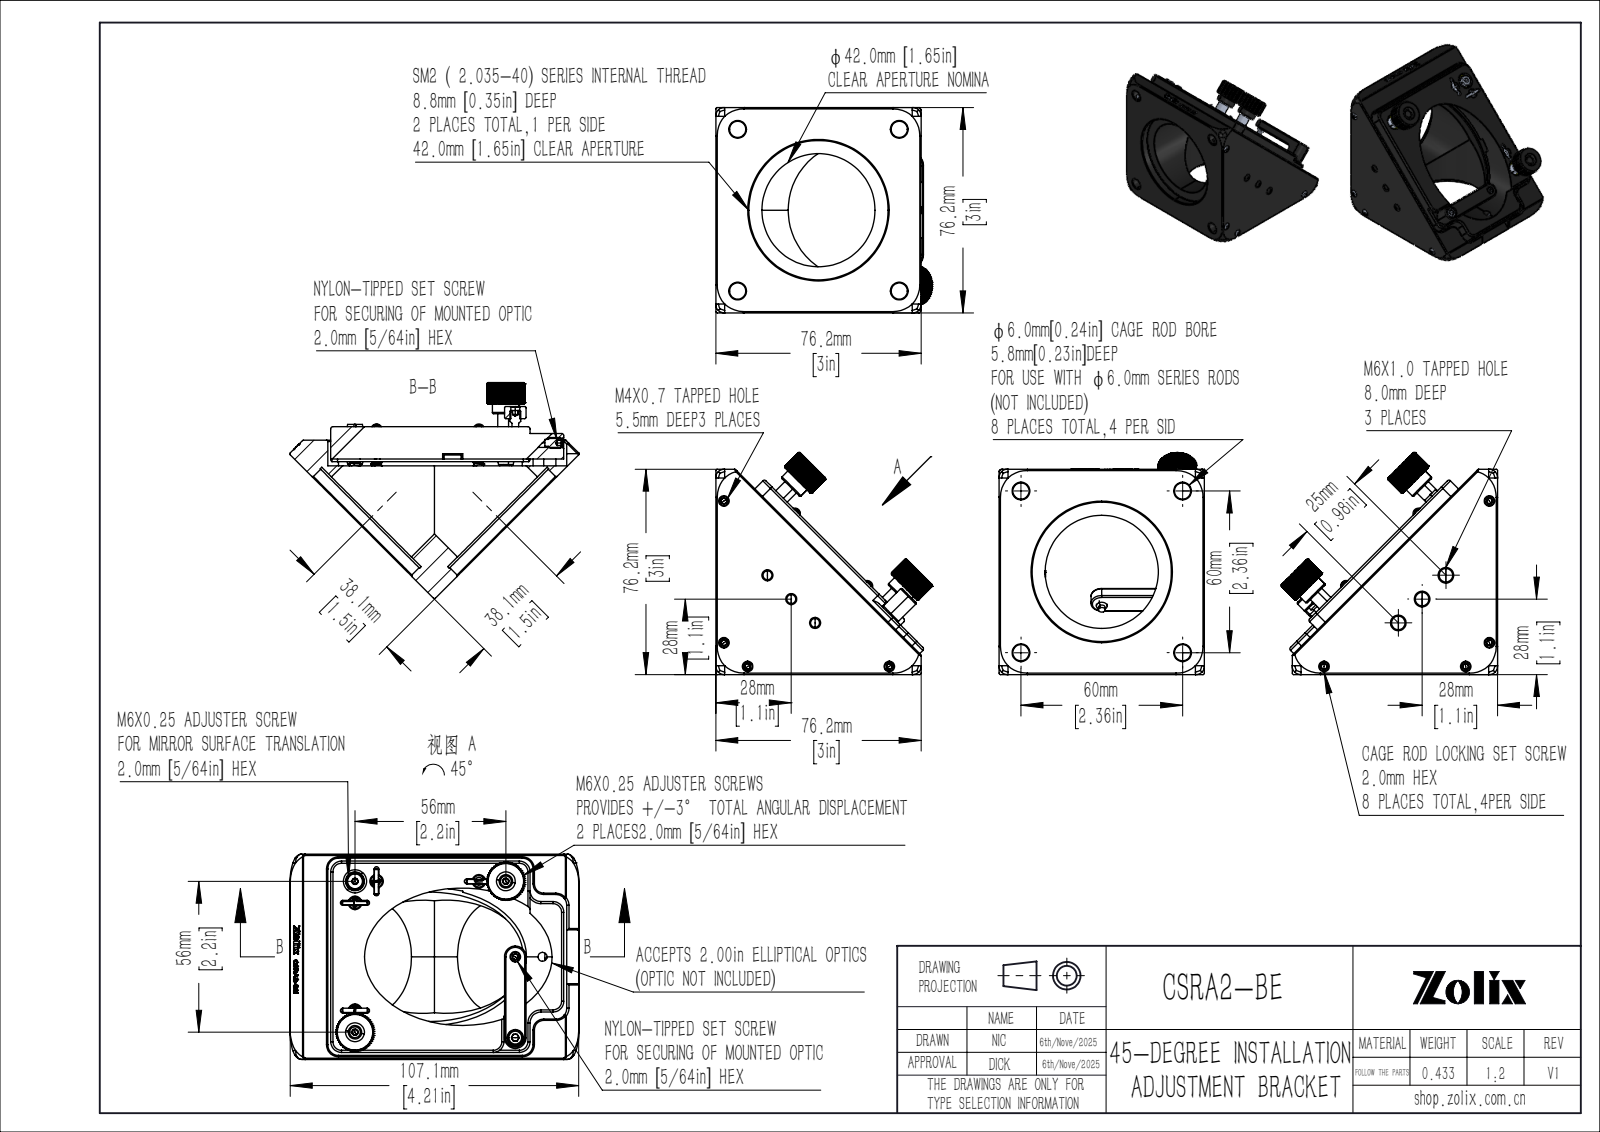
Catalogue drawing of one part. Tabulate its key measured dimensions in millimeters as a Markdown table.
| quantity | value |
| --- | --- |
| part name | CSRA2-BE |
| STEP written by | SolidWorks 2020 (CONFIG_CONTROL_DESIGN) |
| units | millimeters |
| bodies | 40 solids, 2043 faces (916 planar, 525 cylindrical, 602 other) |
| overall size | 82.36 × 80.23 × 76.2 |
| volume | 160 514 mm³ |
| surface area | 60 151 mm² |
| round holes (diameter × count) | 6 × 14, 3.3 × 9, 5 × 7, 2.71 × 4, 5.1 × 4, 1.95 × 3, 4.78 × 3, 8.6 × 3, 9.4 × 3, 1.6 × 2, 2.4 × 2, 2.43 × 2 |
| round bosses / shafts (diameter × count) | 4 × 6, 3.48 × 4, 1.6 × 4, 9.15 × 3, 8.12 × 3, 10 × 2, 3.8 × 2, 2.5 × 2 |
| partial cylindrical surfaces (radius × count) | 0.5 × 63, 4 × 19, 0.8 × 14, 0.9 × 8, 2 × 5, 3 × 4, 0.3 × 2, 7.1 × 2 |
| main face-to-face distances | 2.5, 76.2, 1.5, 5, 12, 13, 1, 1.1, 14.5, 9.5 |
| hole center spacings | 48, 8, 42.43, 60, 56, 56.57, 19.98, 40 |
